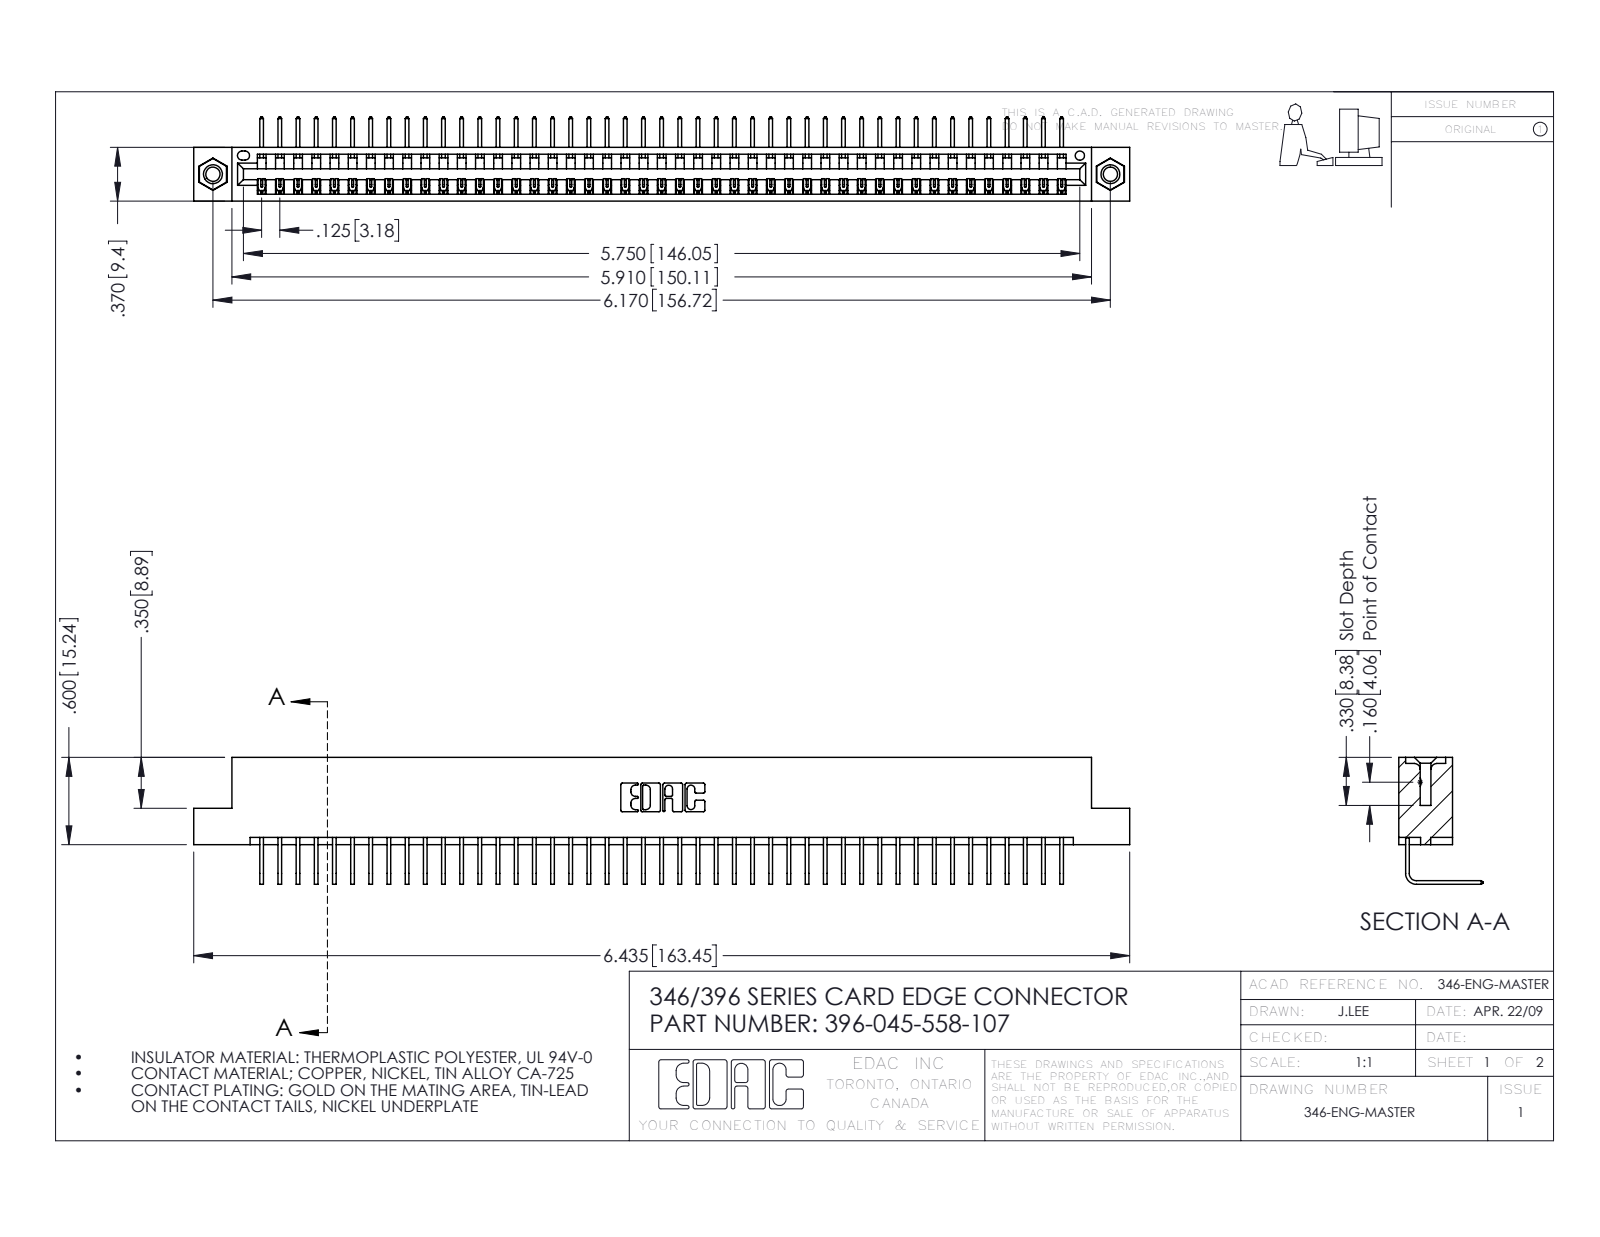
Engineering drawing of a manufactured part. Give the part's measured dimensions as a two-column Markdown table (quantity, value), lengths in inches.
| quantity | value |
| --- | --- |
| part name | 346 Part_Flush Mounting Lugs - 0.156 Dia-TI; 345-292-001_558 Tail - 2; 345-250-001_345-250-005-103; 396-045-558-107 |
| STEP written by | SolidWorks 2016 (CONFIG_CONTROL_DESIGN) |
| units | inches |
| bodies | 48 solids, 2882 faces (1998 planar, 868 cylindrical, 16 other) |
| overall size | 6.435 × 0.873 × 0.58 |
| volume | 0.964 in³ |
| surface area | 32.11 in² |
| round holes (diameter × count) | 0.098 × 2, 0.125 × 2, 0.156 × 2, 0.064 × 1 |
| round bosses / shafts (diameter × count) | 0.155 × 2 |
| partial cylindrical surfaces (radius × count) | 0.006 × 90, 0.01 × 22, 0.007 × 6, 0.031 × 6, 0.026 × 3, 0.031 × 2, 0.04 × 2, 0.014 × 1 |
| main face-to-face distances | 0.322, 0.048, 0.37, 0.25, 0.298, 0.025, 0.072, 0.148, 0.222, 0.1 |
| hole center spacings | 0.246, 5.961, 6.17 |
